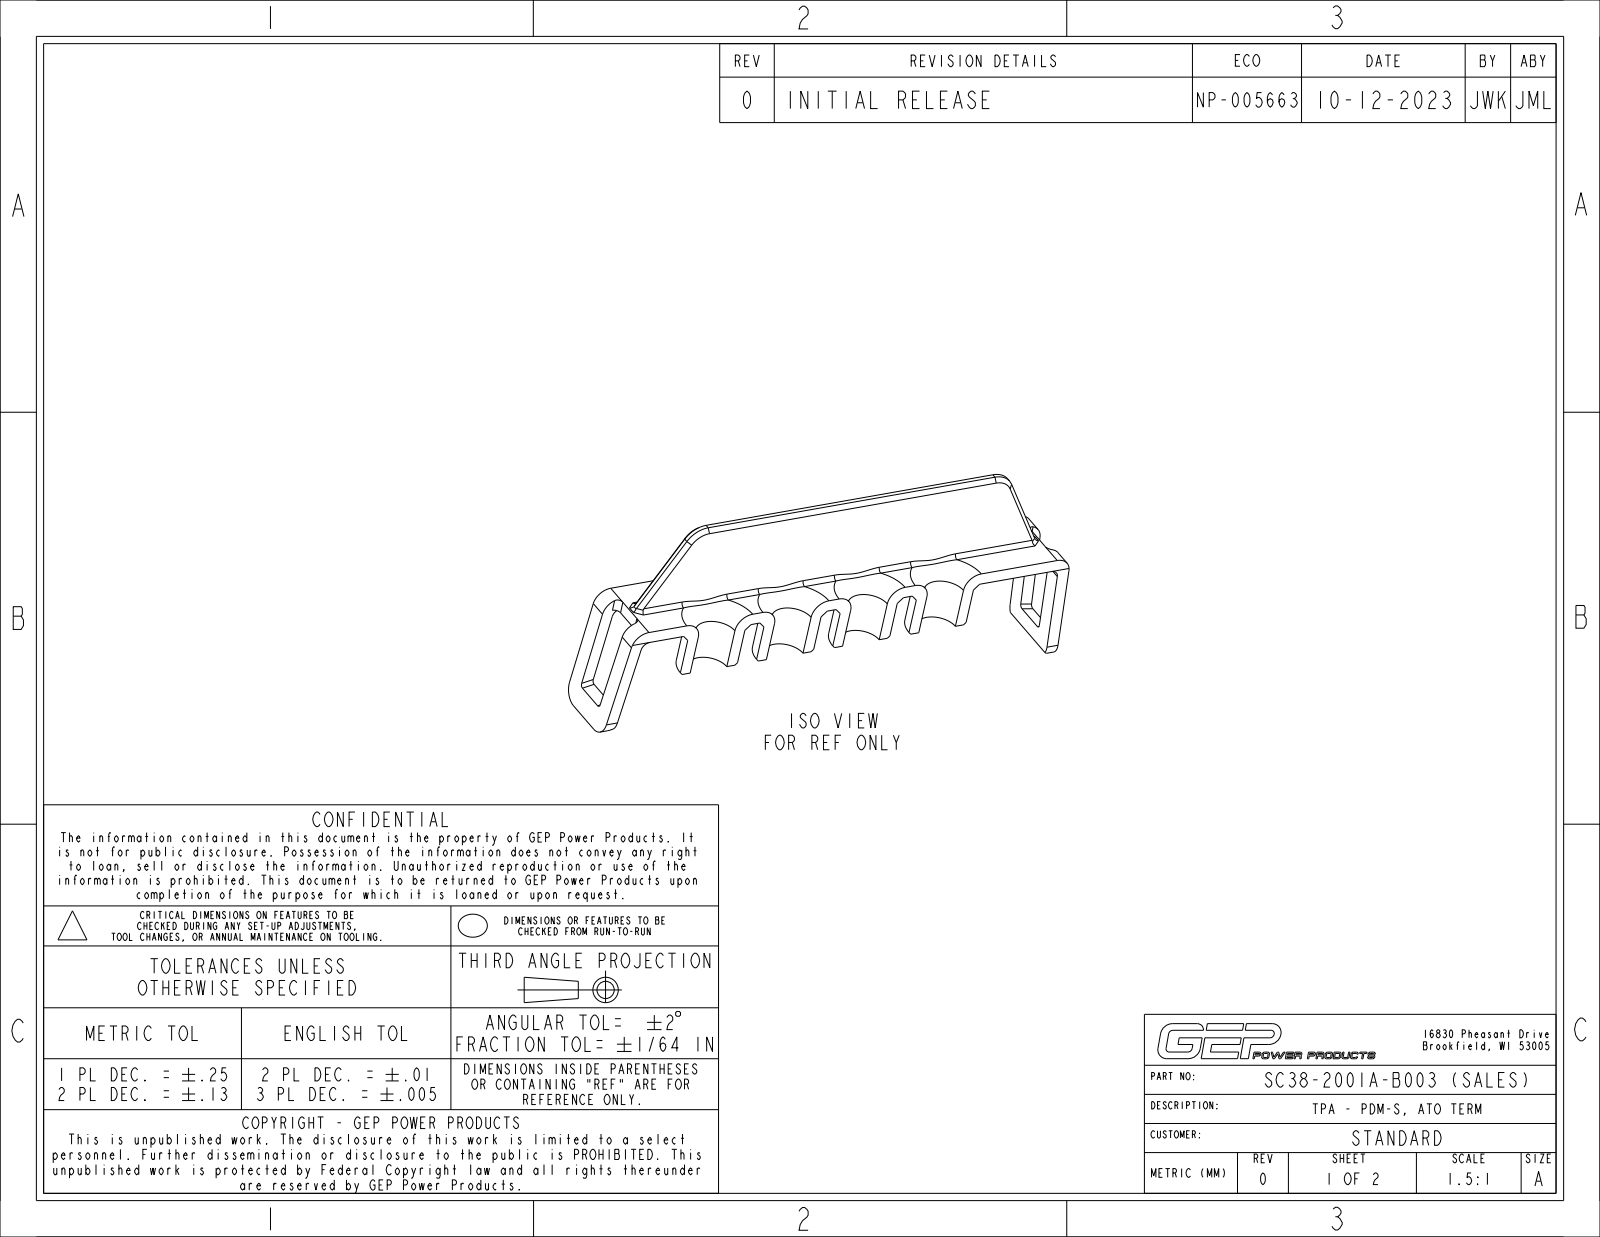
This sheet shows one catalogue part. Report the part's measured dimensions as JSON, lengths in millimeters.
{"part_name": "PC38-2001A-B003_NCF; SC38-2001A-B003_NCF_ASM", "step_written_by": "CREO PARAMETRIC BY PTC INC, 2017110 (CONFIG_CONTROL_DESIGN)", "units": "millimeters", "bodies": {"solids": 1, "faces": 189, "planar": 93, "cylindrical": 60, "other": 36}, "overall_size": [61.99, 25.3, 9.1], "volume_mm3": 2216, "surface_area_mm2": 3470, "round_bosses_or_shafts": [[3, 1]], "partial_cylinders_radius": [[0.5, 12], [2.5, 8], [3.9, 8], [0.4, 4], [0.7, 4], [2, 4], [1, 2], [3, 2]], "face_to_face_distances": [1.5, 3.8, 5.3, 9.1, 5.65, 7.15, 2.2, 17.65, 12, 10.5]}
